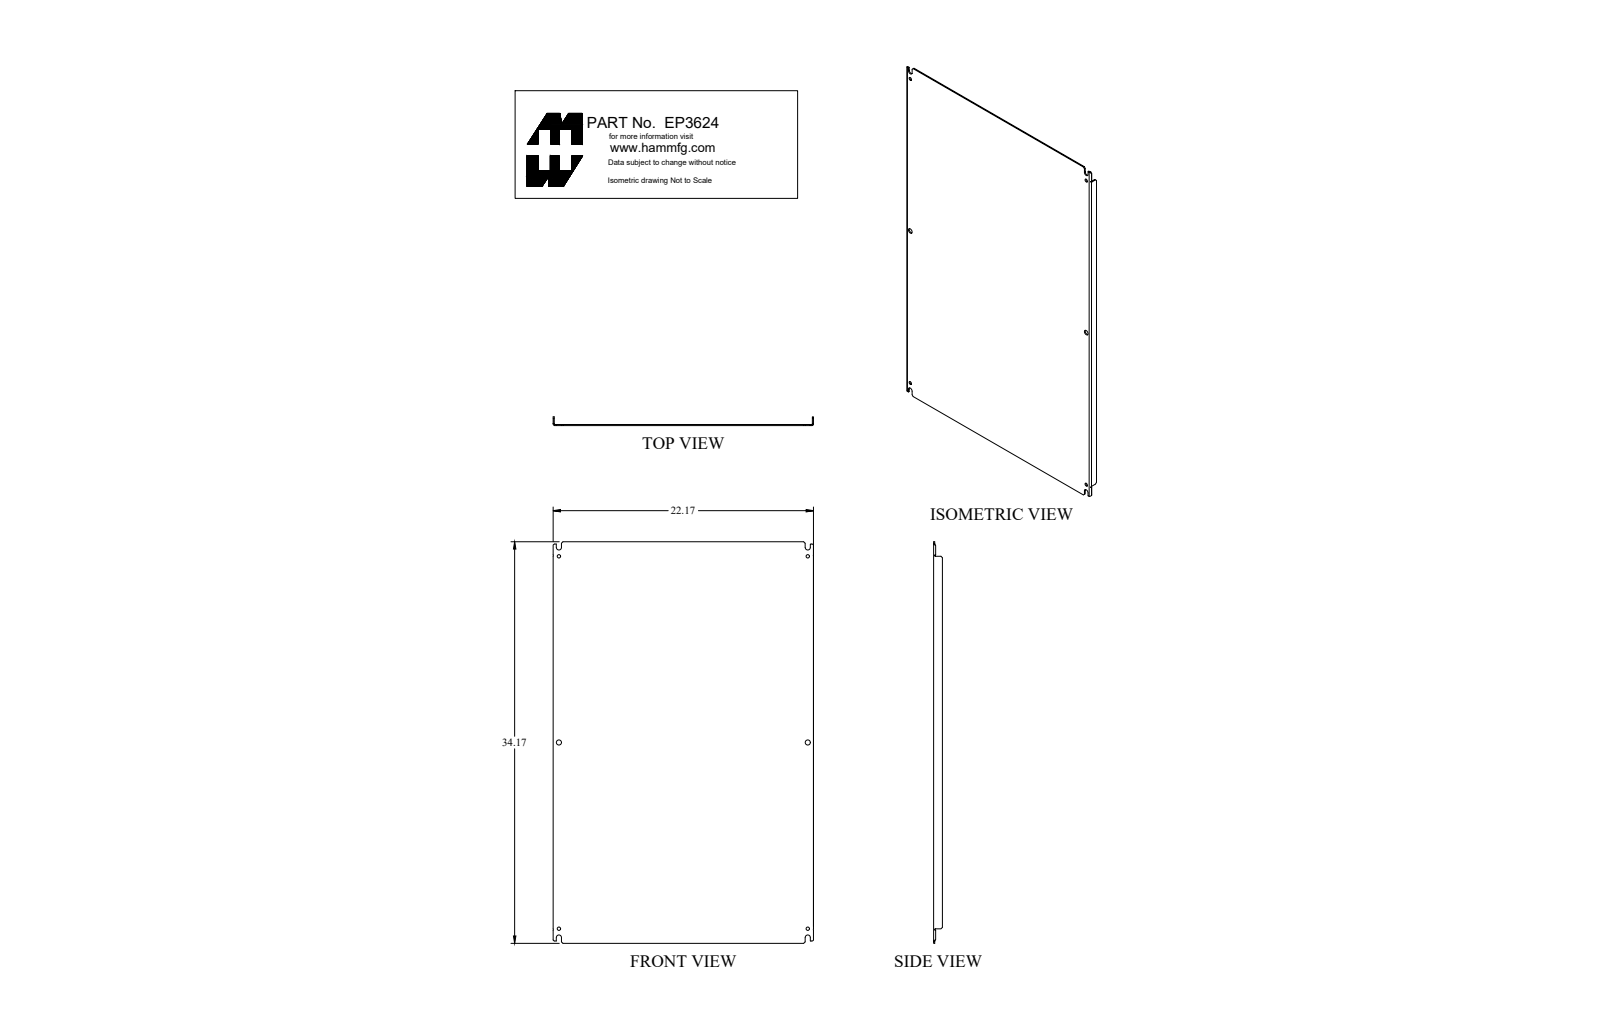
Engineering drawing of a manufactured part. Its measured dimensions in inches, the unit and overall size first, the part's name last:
Units: inches
Overall size (bounding box): 34.17 × 22.17 × 0.75
Round holes (diameter × count): ⌀0.281 ×4, ⌀0.437 ×2
Partial cylindrical surfaces — rounded edges, fillets, slot ends (radius × count): R0.219 ×4, R0.048 ×2, R0.063 ×2, R0.143 ×2
Main face-to-face distances: 0.095, 22.075, 21.98, 22.17, 0.75, 0.655, 34.17, 0.171, 0.076, 0.579
Hole centre spacings: 15.844, 26.457, 21.188, 31.688, 38.119
Volume: 75.48 in³ · Surface area: 1 601 in²
Bodies: 1 solid, 88 faces (50 planar, 30 cylindrical, 8 other)
Part name (STEP PRODUCT): EP3624
STEP written by: SolidWorks 2018 (AUTOMOTIVE_DESIGN)
